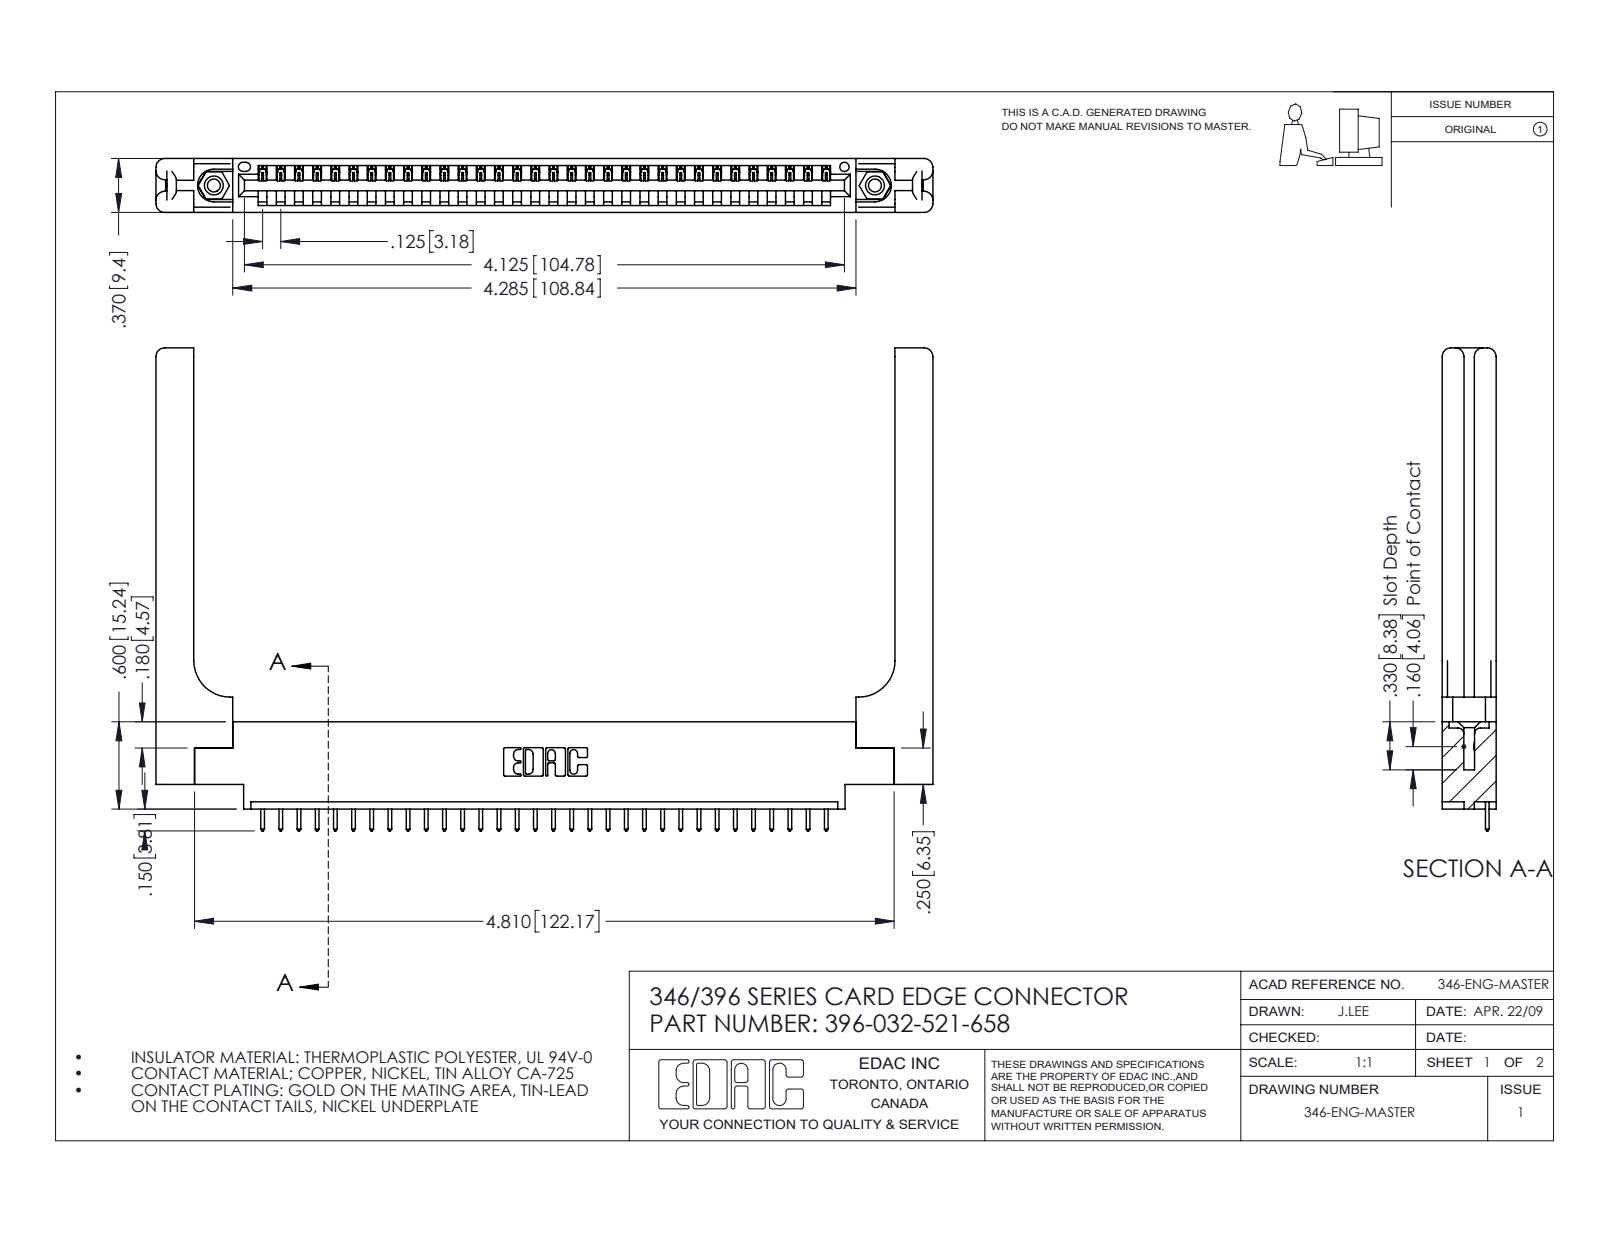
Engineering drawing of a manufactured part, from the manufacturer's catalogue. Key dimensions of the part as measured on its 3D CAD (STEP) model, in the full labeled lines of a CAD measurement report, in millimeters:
Part name (STEP PRODUCT): 345-292-001_345-293-121; 396-032-521-658; 346-220-058_345-220-058; 346 Part_0.170 Offset - 0.156 Dia-TH (+1 more)
STEP written by: SolidWorks 2016 (CONFIG_CONTROL_DESIGN)
Units: millimetres
Bodies: 37 solids, 2238 faces (1508 planar, 670 cylindrical, 60 other)
Overall size (bounding box): 135.7 × 84.3 × 9.4
Volume: 20 190 mm³ · Surface area: 20 700 mm²
Round holes (diameter × count): ⌀2.3 ×2, ⌀3.2 ×2, ⌀4 ×2, ⌀1.6 ×1
Round bosses / shafts (diameter × count): ⌀3.9 ×2
Partial cylindrical surfaces — rounded edges, fillets, slot ends (radius × count): R0.2 ×64, R0.3 ×64, R0.3 ×22, R1.5 ×16, R0.2 ×6, R0.8 ×6, R0.7 ×3, R0.8 ×2
Main face-to-face distances: 9.4, 1.2, 8.2, 1.8, 3.8, 3.8, 6.4, 7.6, 0.6, 5.6
Hole centre spacings: 6.2, 110.2, 115.4
